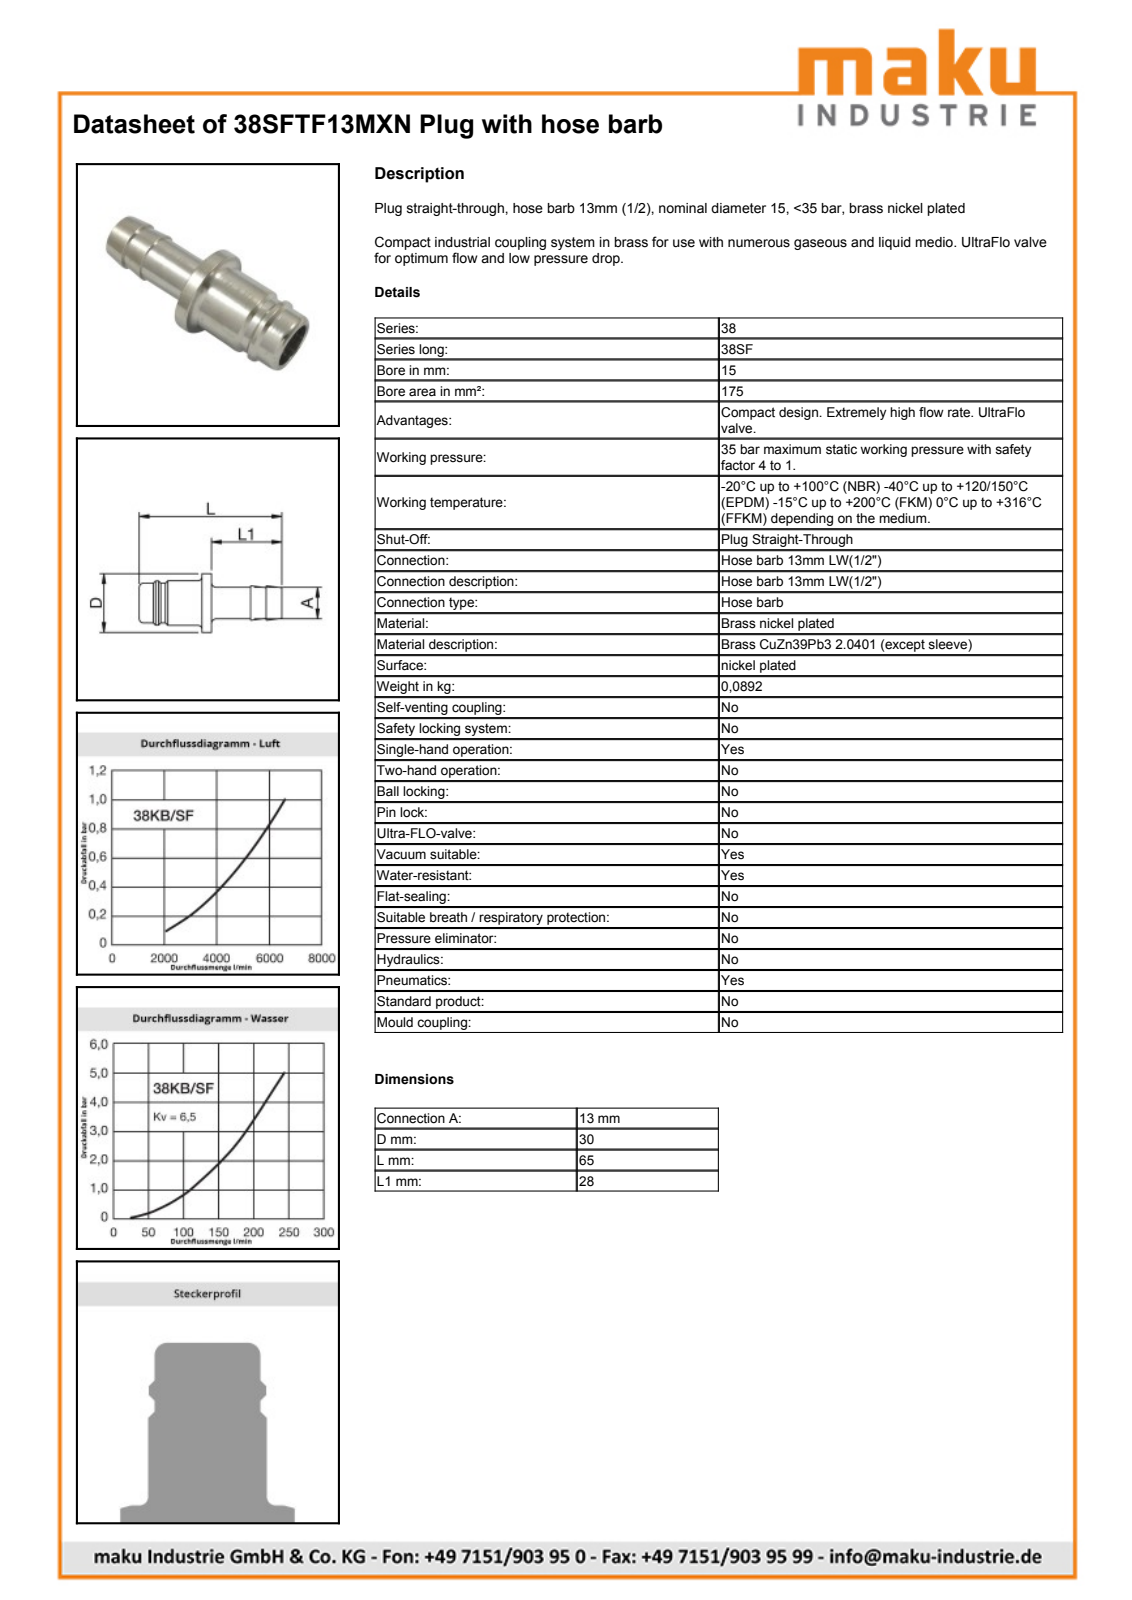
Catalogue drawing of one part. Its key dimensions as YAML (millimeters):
part_name: "D110621"
step_written_by: "Autodesk Inventor 2013 (AUTOMOTIVE_DESIGN)"
units: millimeters
bodies: {solids: 1, faces: 28, planar: 6, cylindrical: 8, other: 14}
overall_size: [65, 30, 30]
volume: 10564
surface_area: 7548
round_holes:
  - {diameter: 11, count: 1}
  - {diameter: 15, count: 1}
round_bosses_or_shafts:
  - {diameter: 30, count: 1}
  - {diameter: 22.85, count: 1}
  - {diameter: 22.6, count: 1}
  - {diameter: 20.3, count: 1}
  - {diameter: 13.05, count: 1}
face_to_face_distances: [4.9, 6, 32.1, 37, 59, 26.9, 22, 65, 32.9, 28]
